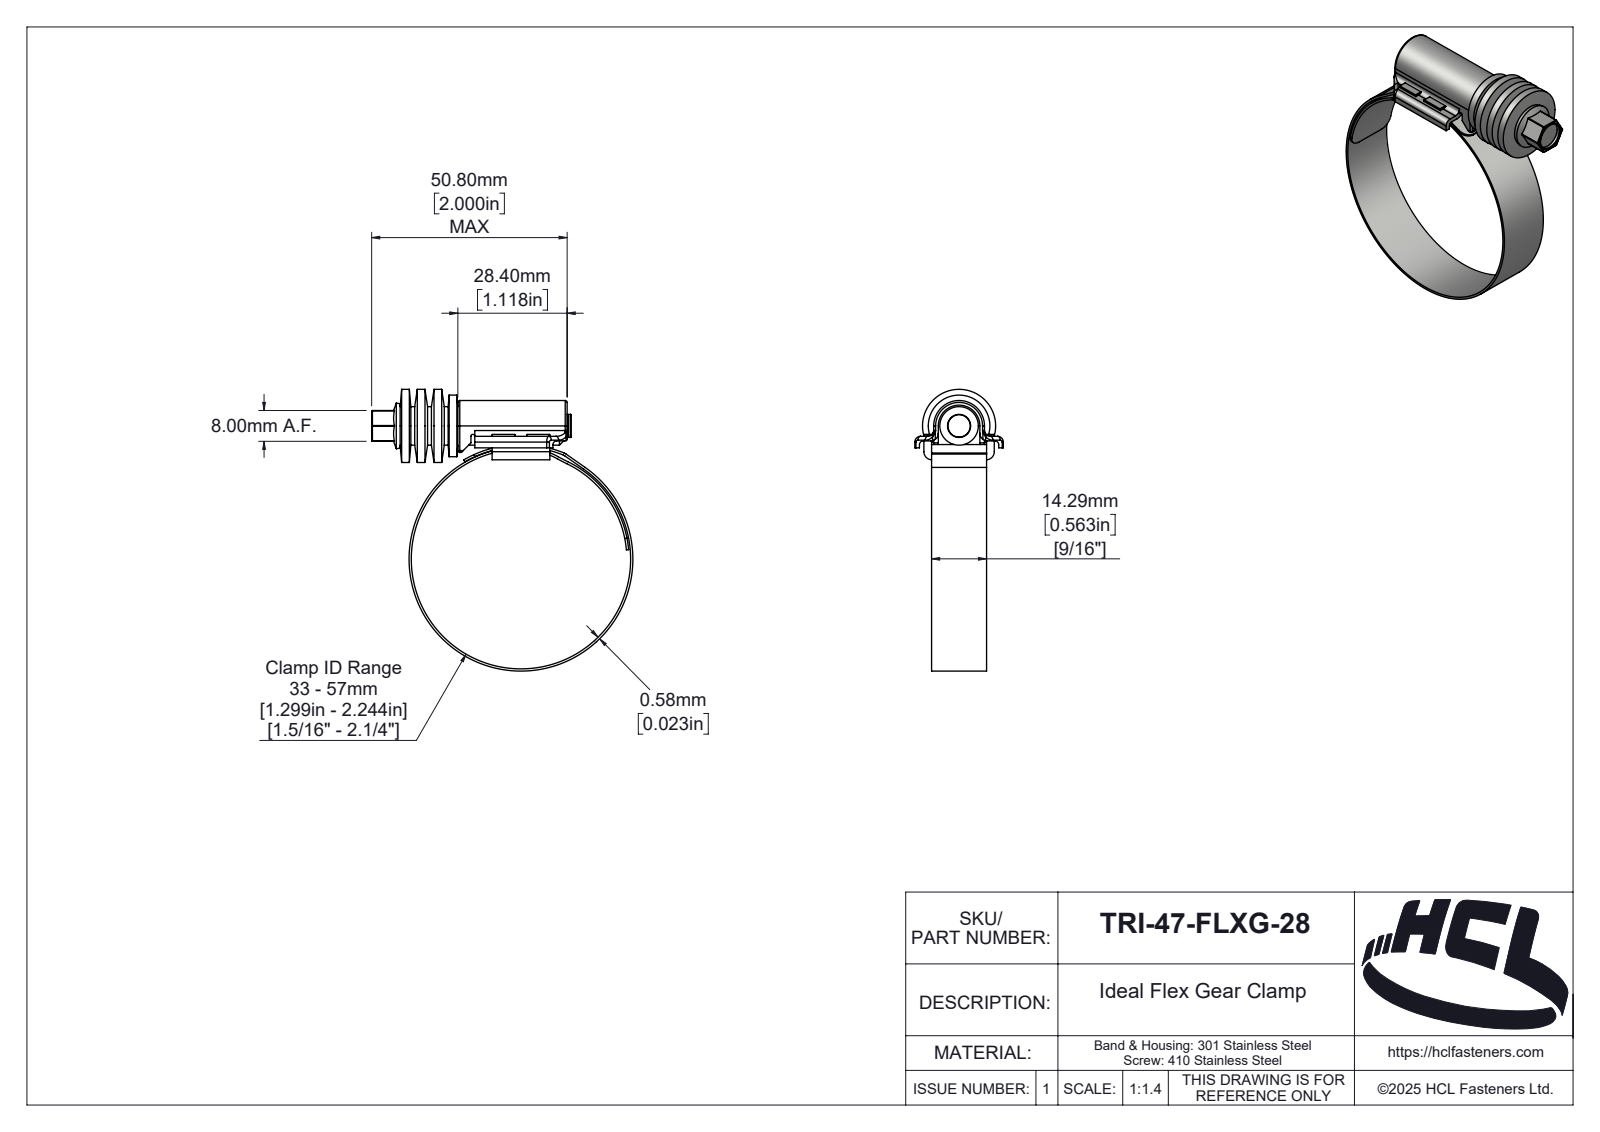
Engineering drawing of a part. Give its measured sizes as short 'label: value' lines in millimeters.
name: TRI-47-FLXG-28
written by: SolidWorks 2025 (AUTOMOTIVE_DESIGN)
unit: mm
bodies: 4 solids, 323 faces (88 planar, 139 cylindrical, 96 other)
size: 73.18 × 67.88 × 23
volume: 9 552 mm³; area: 13 532 mm²
holes: 1× ⌀7, 1× ⌀57
bosses: 1× ⌀58.16, 1× ⌀19, 1× ⌀16, 1× ⌀10, 1× ⌀6, 1× ⌀5
rounds: 12× R0.2, 9× R0.5, 8× R1, 4× R1.5, 4× R3, 3× R2, 2× R0.1, 2× R2.1
face distances: 2, 1.2, 14.28, 4.9, 1.74, 12.54, 16.29, 6.1, 0.54, 13.74
